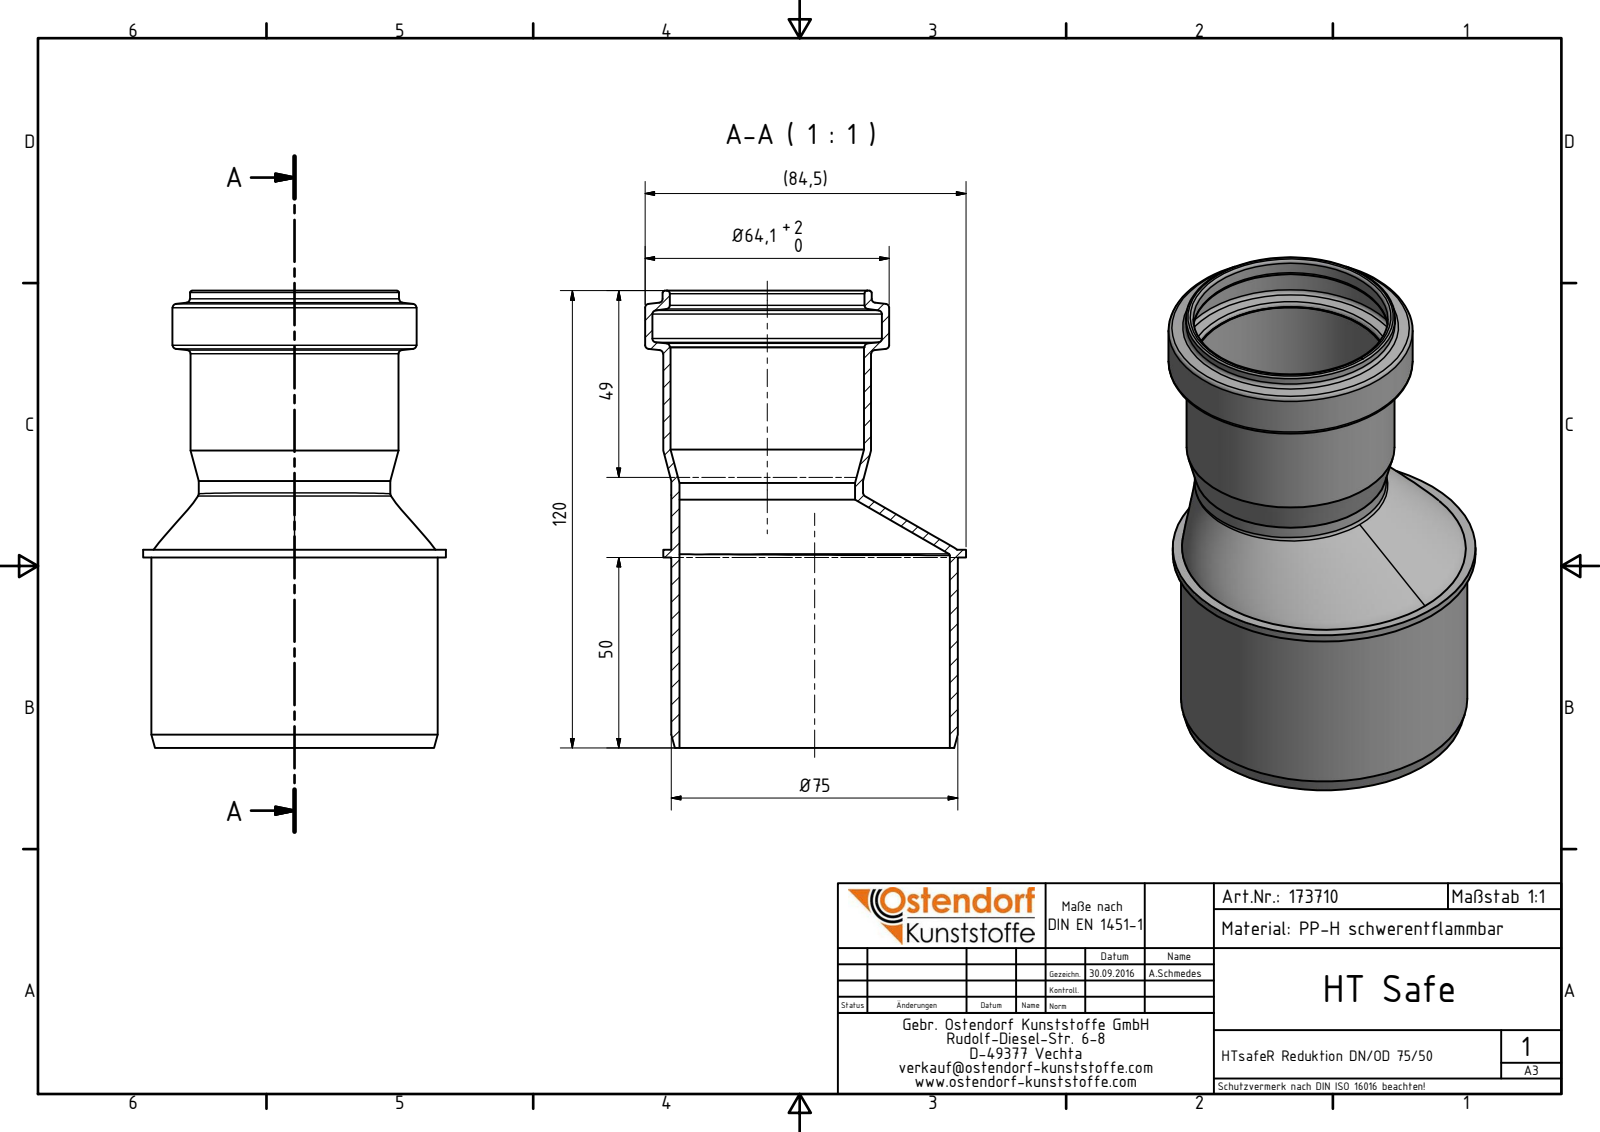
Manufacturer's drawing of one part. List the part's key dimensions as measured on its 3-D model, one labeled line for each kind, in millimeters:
Part name (STEP PRODUCT): 173710 HTsafeR DN_OD 75_50
STEP written by: Autodesk Inventor 2016 (AUTOMOTIVE_DESIGN)
Units: millimetres
Bodies: 1 solid, 38 faces (5 planar, 12 cylindrical, 21 other)
Overall size (bounding box): 120 × 84.25 × 79.5
Volume: 54 047 mm³ · Surface area: 53 922 mm²
Round holes (diameter × count): ⌀46.1 ×1, ⌀50.8 ×1, ⌀51.1 ×1, ⌀60.3 ×1, ⌀71 ×1
Round bosses / shafts (diameter × count): ⌀79.5 ×1, ⌀75.2 ×1, ⌀64.1 ×1, ⌀54.9 ×1, ⌀54.6 ×1, ⌀50.3 ×1
Main face-to-face distances: 2, 50, 52, 120, 70, 68, 105.1, 55.1, 53.1, 14.9
Hole centre spacings: 12.45
